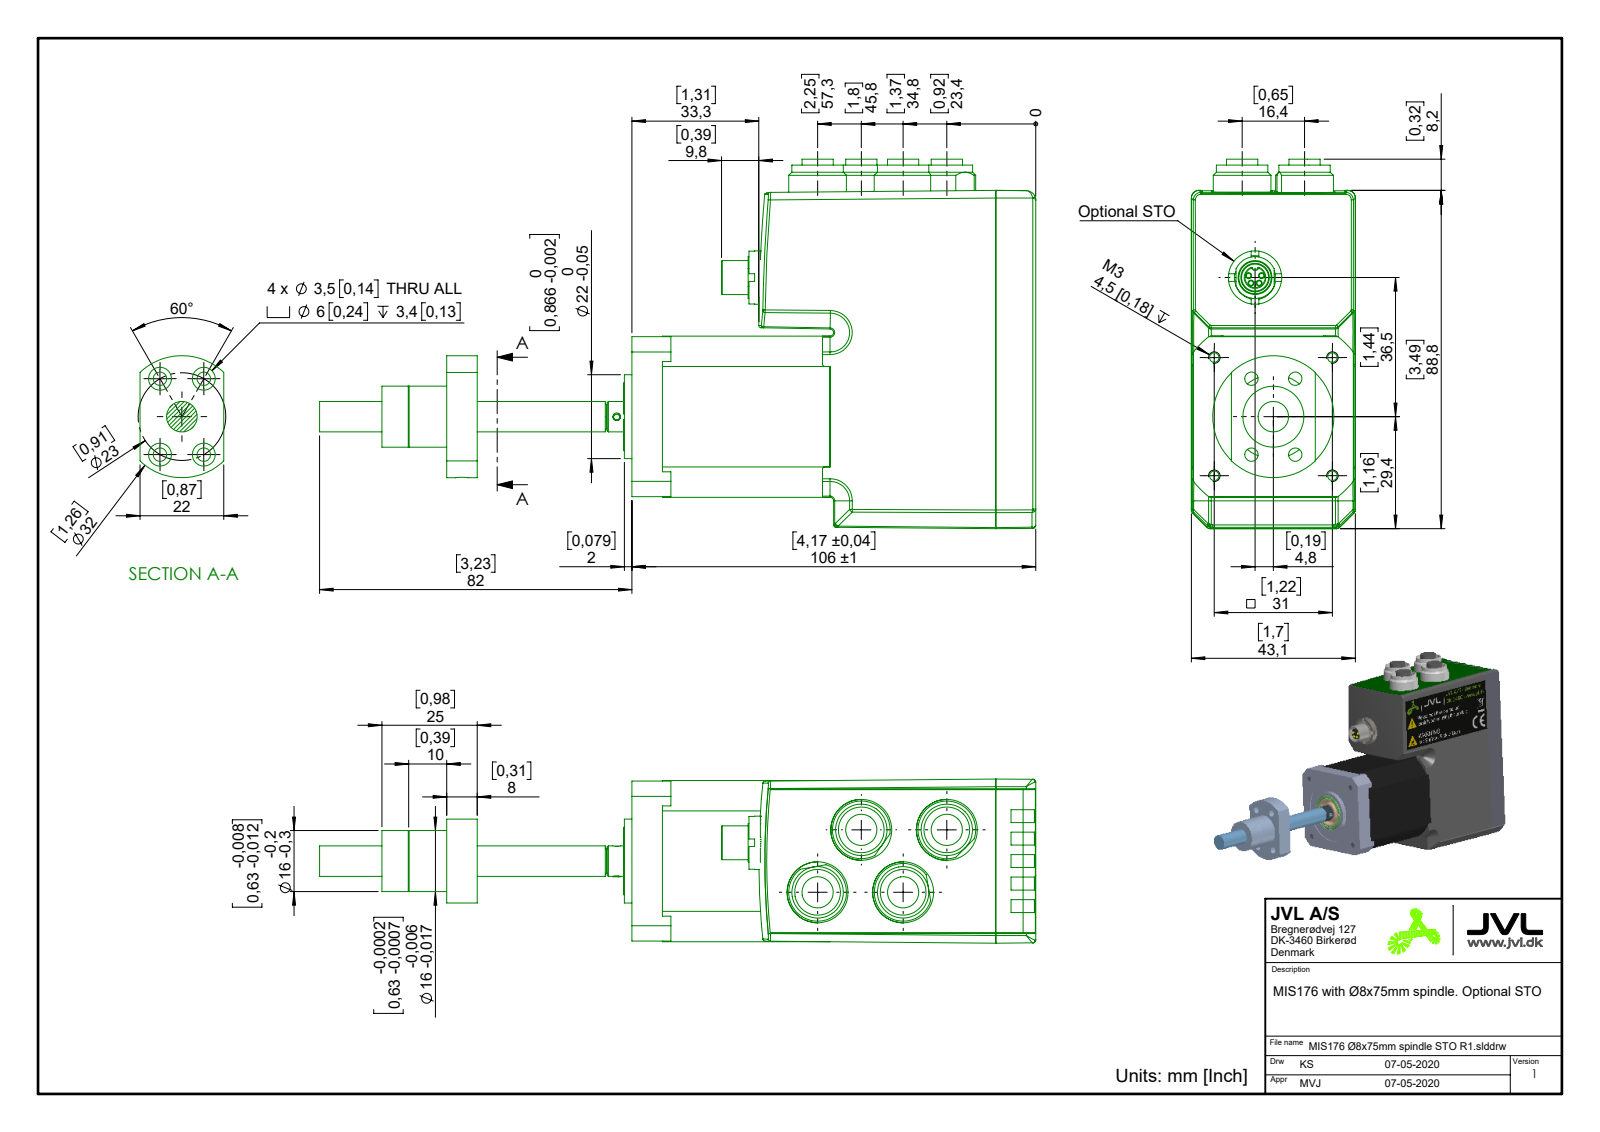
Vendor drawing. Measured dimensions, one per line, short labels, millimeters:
name: MIS176 Ø8x75mm spindle STO R1
written by: SolidWorks 2018 (AUTOMOTIVE_DESIGN)
unit: mm
bodies: 6 solids, 695 faces (271 planar, 272 cylindrical, 152 other)
size: 188 × 96.94 × 43.06
volume: 331 697 mm³; area: 45 156 mm²
holes: 4× ⌀1.2, 4× ⌀2.5, 4× ⌀3.5, 4× ⌀6, 4× ⌀12, 4× ⌀16, 3× ⌀3.3, 1× ⌀2, 1× ⌀6.35, 1× ⌀7.1, 1× ⌀8.3, 1× ⌀9
bosses: 4× ⌀15.15, 4× ⌀13.5, 4× ⌀8.2, 4× ⌀1.6, 4× ⌀0.8, 1× ⌀22, 1× ⌀16, 1× ⌀15.5
rounds: 30× R1, 4× R0.8, 2× R0.2, 2× R0.93, 2× R2, 2× R3.8, 2× R4.2, 1× R0.35
face distances: 42.3, 43.07, 42.15, 105.9, 42, 106, 8, 2, 40.63, 146.53
hole spacings: 11.5, 11.21, 20, 21.92, 21.96, 22.45, 27.26, 31
